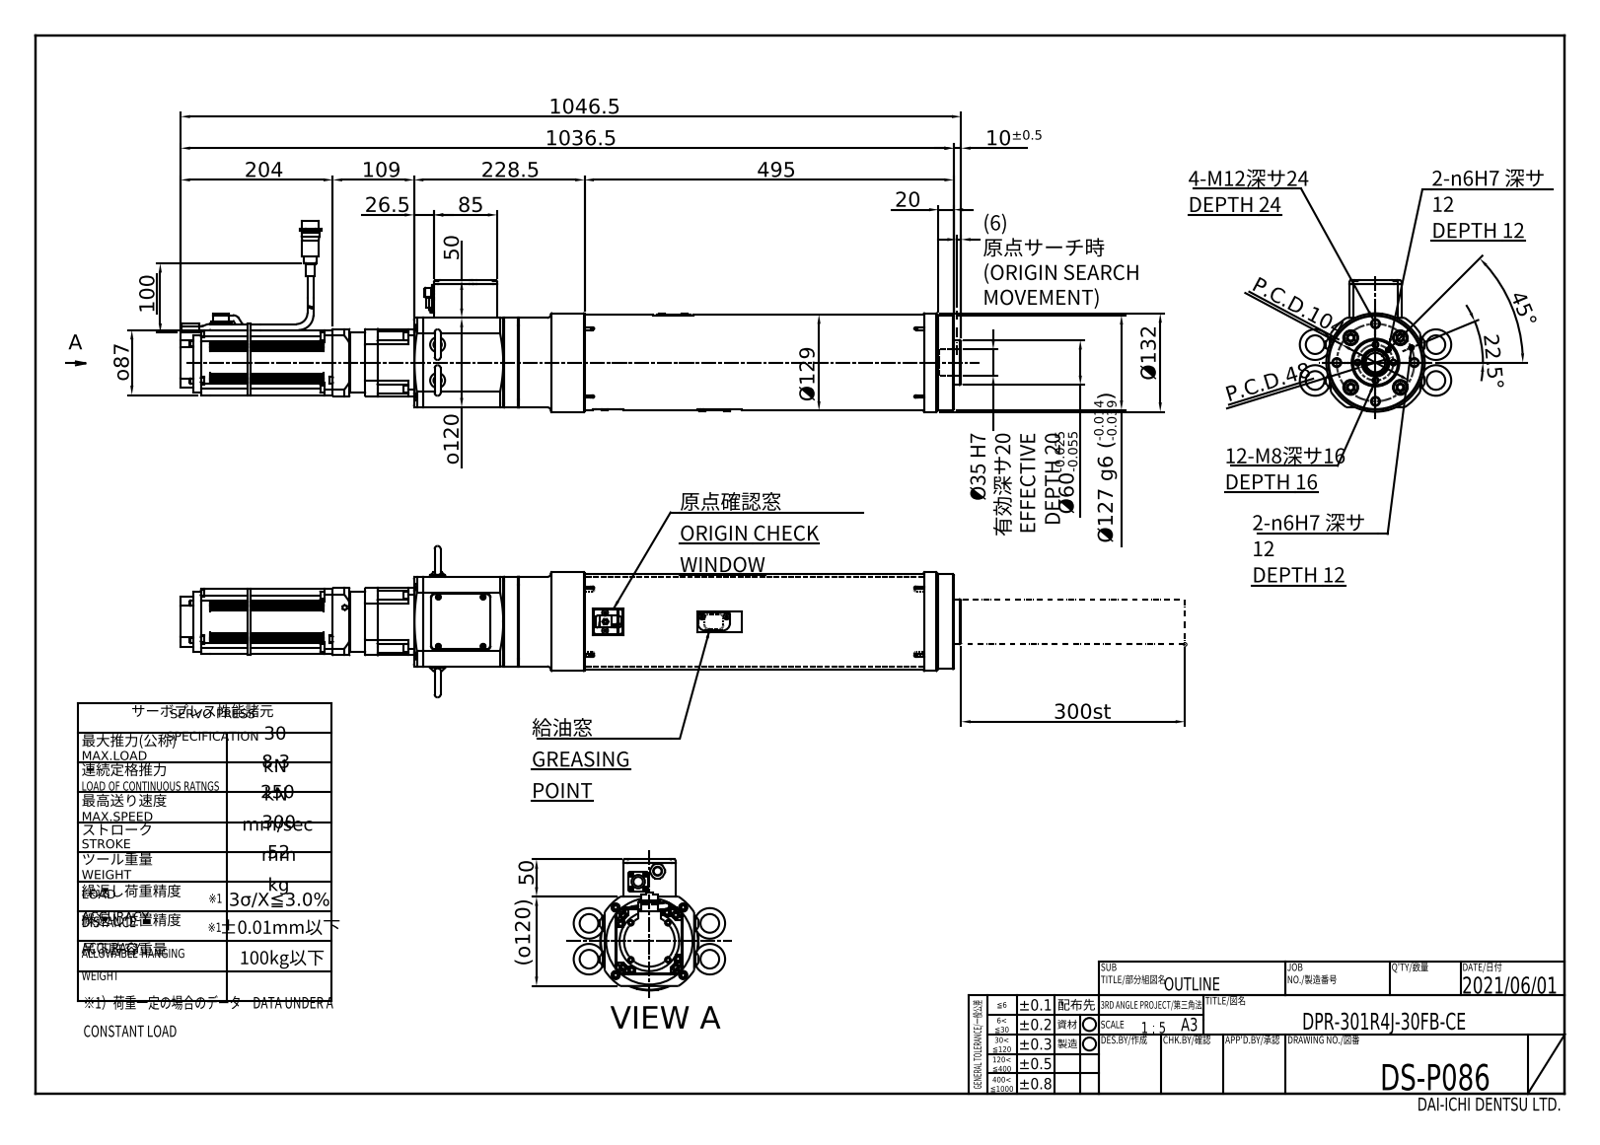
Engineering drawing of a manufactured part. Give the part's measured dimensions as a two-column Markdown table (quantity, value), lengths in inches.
| quantity | value |
| --- | --- |
| part name | DPR-301R4J-30FB-CE(DS-P086) |
| STEP written by | Autodesk Inventor 2021 (AUTOMOTIVE_DESIGN) |
| units | inches |
| bodies | 1 solid, 1822 faces (1033 planar, 458 cylindrical, 331 other) |
| overall size | 41.201 × 7.992 × 6.929 |
| volume | 716.4 in³ |
| surface area | 890.5 in² |
| round holes (diameter × count) | 0.097 × 4, 0.122 × 4, 0.126 × 4, 0.13 × 4, 0.134 × 4, 0.194 × 4, 0.266 × 4, 0.315 × 4, 0.33 × 4, 0.354 × 4, 0.404 × 4, 0.433 × 4 |
| round bosses / shafts (diameter × count) | 0.315 × 12, 0.394 × 8, 0.335 × 8, 0.236 × 8, 0.709 × 5, 1.614 × 4, 0.295 × 4, 0.276 × 4 |
| partial cylindrical surfaces (radius × count) | 0.024 × 48, 0.197 × 41, 0.039 × 28, 0.02 × 19, 0.079 × 18, 0.098 × 12, 0.118 × 12, 0.059 × 7 |
| main face-to-face distances | 0.059, 0.65, 3.484, 0.591, 3.425, 4.075, 0.118, 2.835, 4.134, 0.709 |
| hole center spacings | 1.502, 1.539, 1.801, 2.702, 3.126, 3.197, 3.602, 3.71 |
